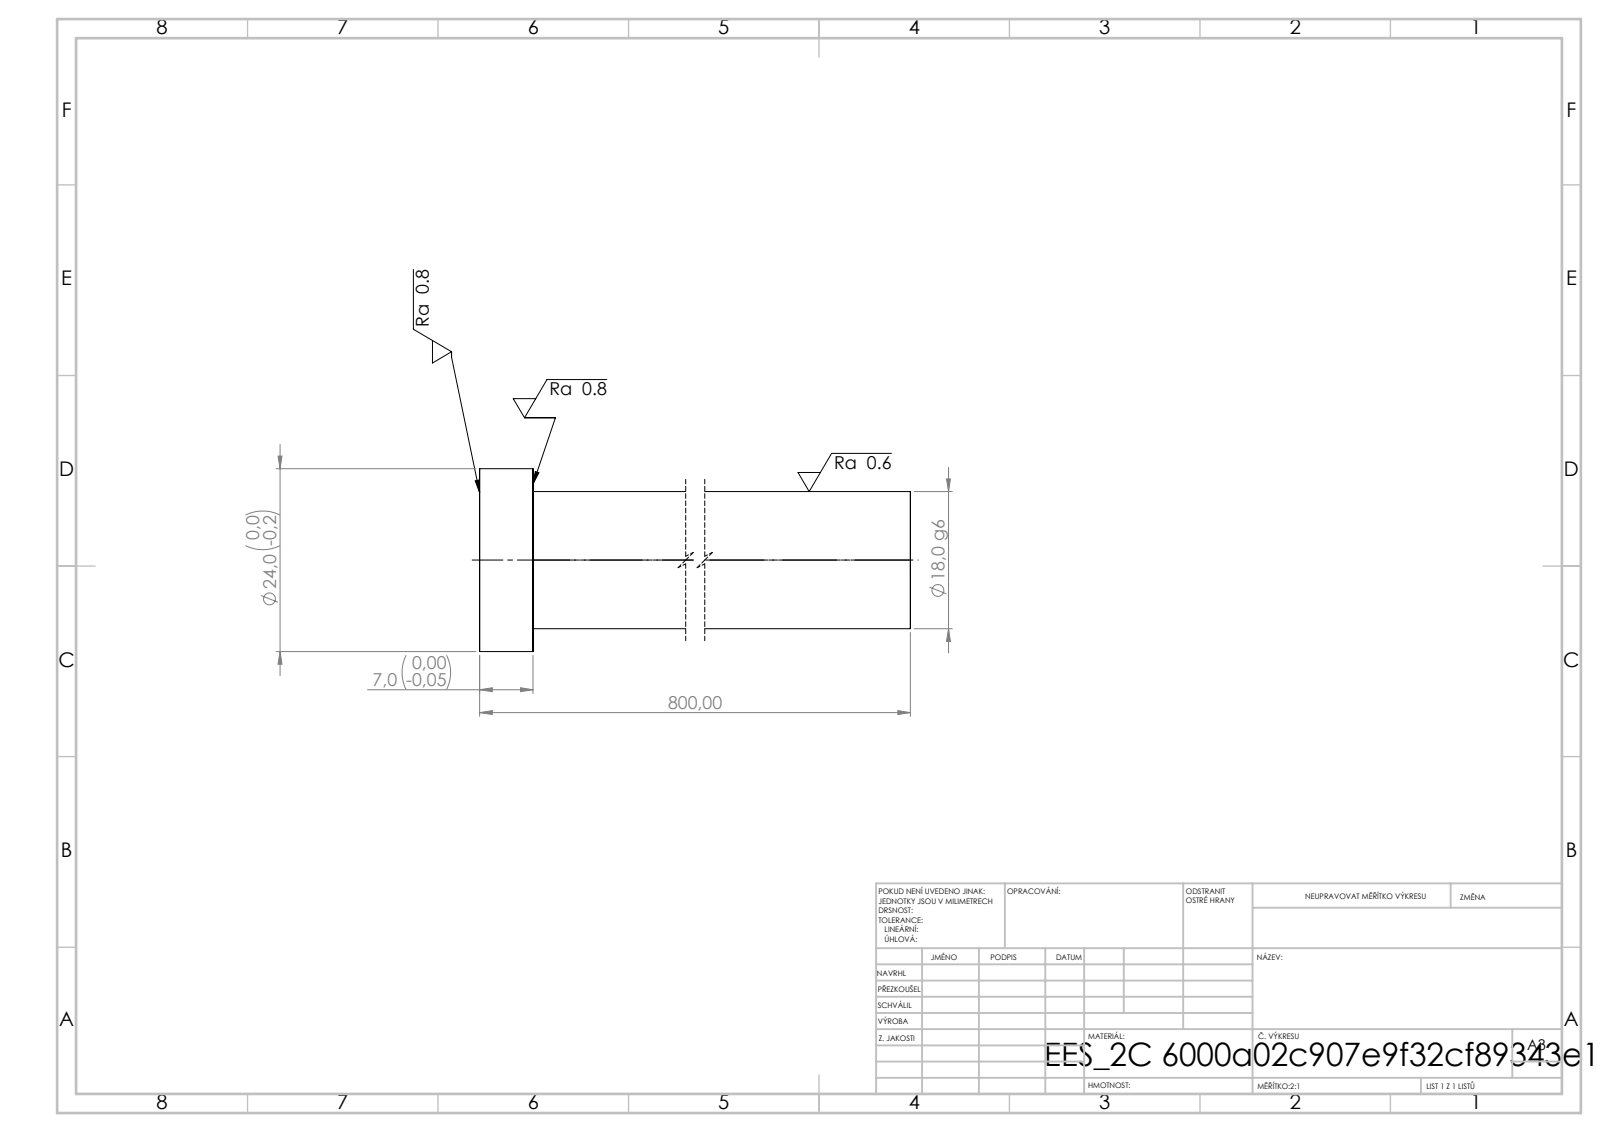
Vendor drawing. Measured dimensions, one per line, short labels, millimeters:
written by: SolidWorks 2019 (CONFIG_CONTROL_DESIGN)
unit: mm
bodies: 1 solid, 7 faces (3 planar, 4 cylindrical, 0 other)
size: 800 × 24 × 24
volume: 204 961 mm³; area: 46 276 mm²
bosses: 1× ⌀24, 1× ⌀18
face distances: 800, 7, 793
